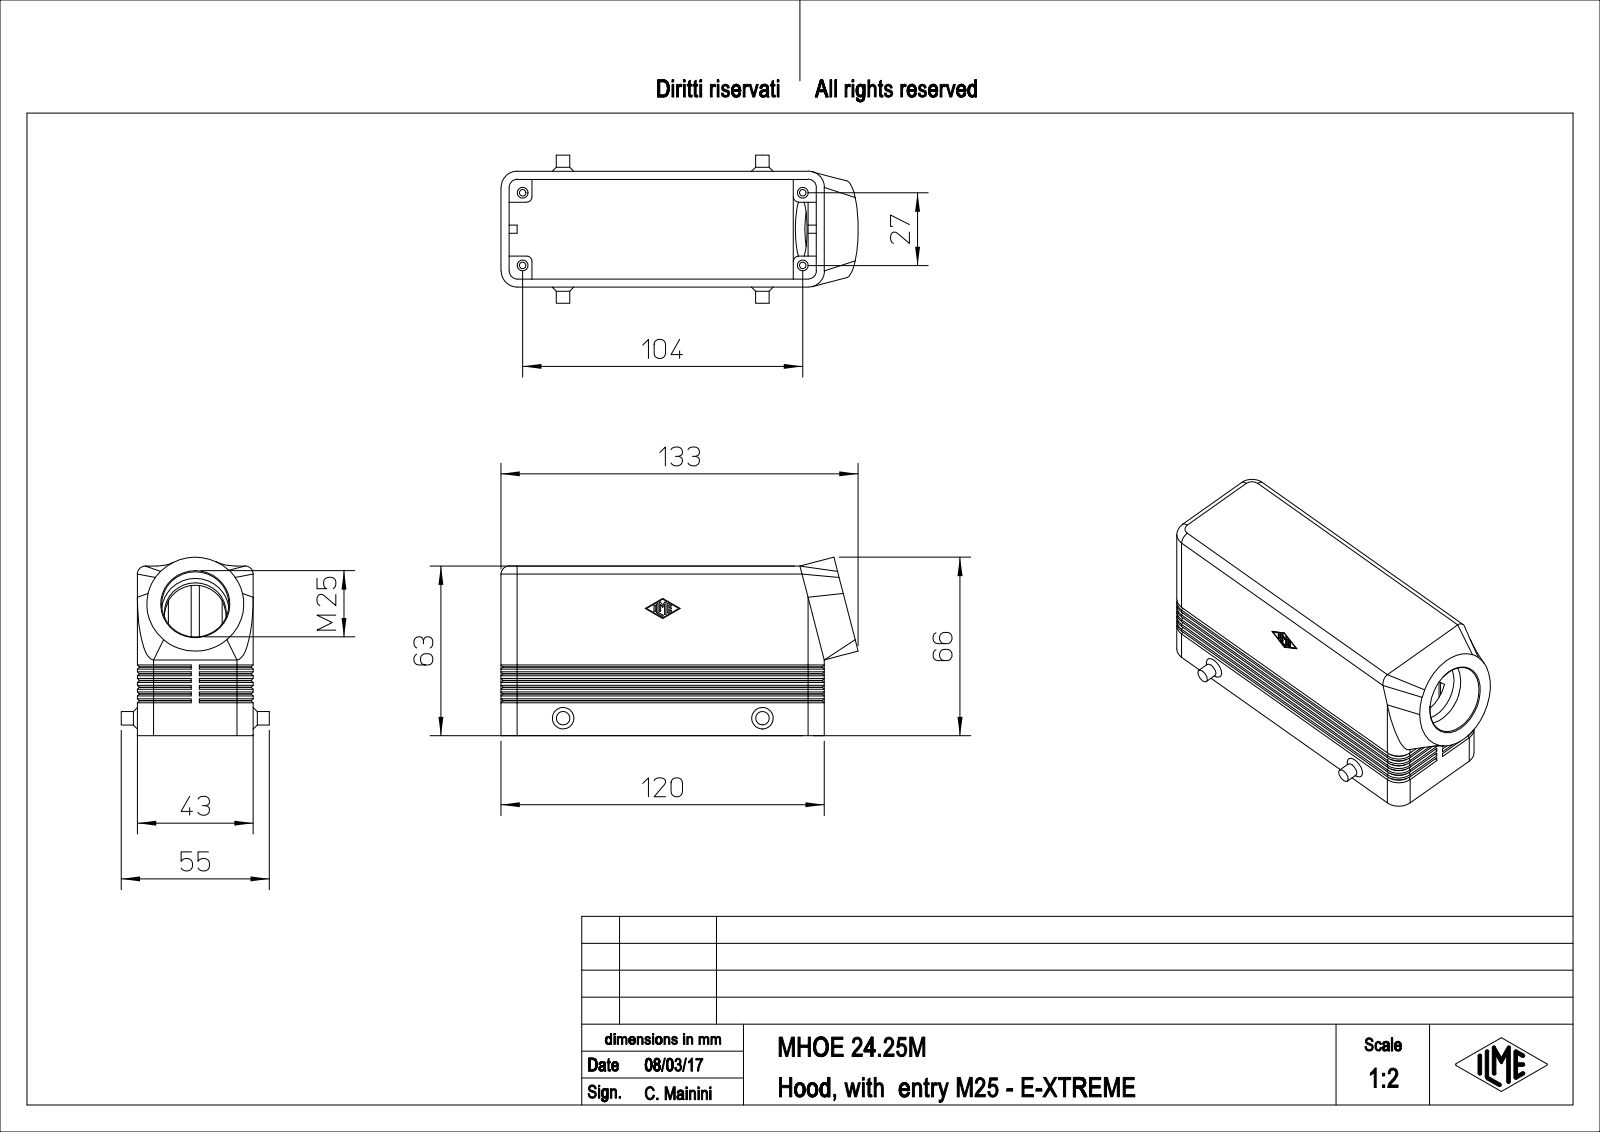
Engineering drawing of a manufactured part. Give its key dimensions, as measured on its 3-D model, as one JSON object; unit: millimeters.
{"part_name": "MHOE_24.25M", "step_written_by": "PTC Creo Elements/Direct Modeling 19.0E 27-Jun-2016 (C) Parametric Technology GmbH (AUTOMOTIVE_DESIGN)", "units": "millimeters", "bodies": {"solids": 1, "faces": 408, "planar": 223, "cylindrical": 107, "other": 78}, "overall_size": [132.59, 66.25, 55], "volume_mm3": 89180, "surface_area_mm2": 50684, "round_holes": [[2.46, 4], [4, 4], [23, 1], [25, 1]], "round_bosses_or_shafts": [[5, 2]], "partial_cylinders_radius": [[0.25, 14], [3, 7], [2, 4], [5.3, 4], [6, 4], [1.5, 1]], "face_to_face_distances": [3, 40, 37, 43, 8.5, 11.5, 1.77, 5.3, 20, 105.5], "hole_center_spacings": [27, 104, 107.45]}
